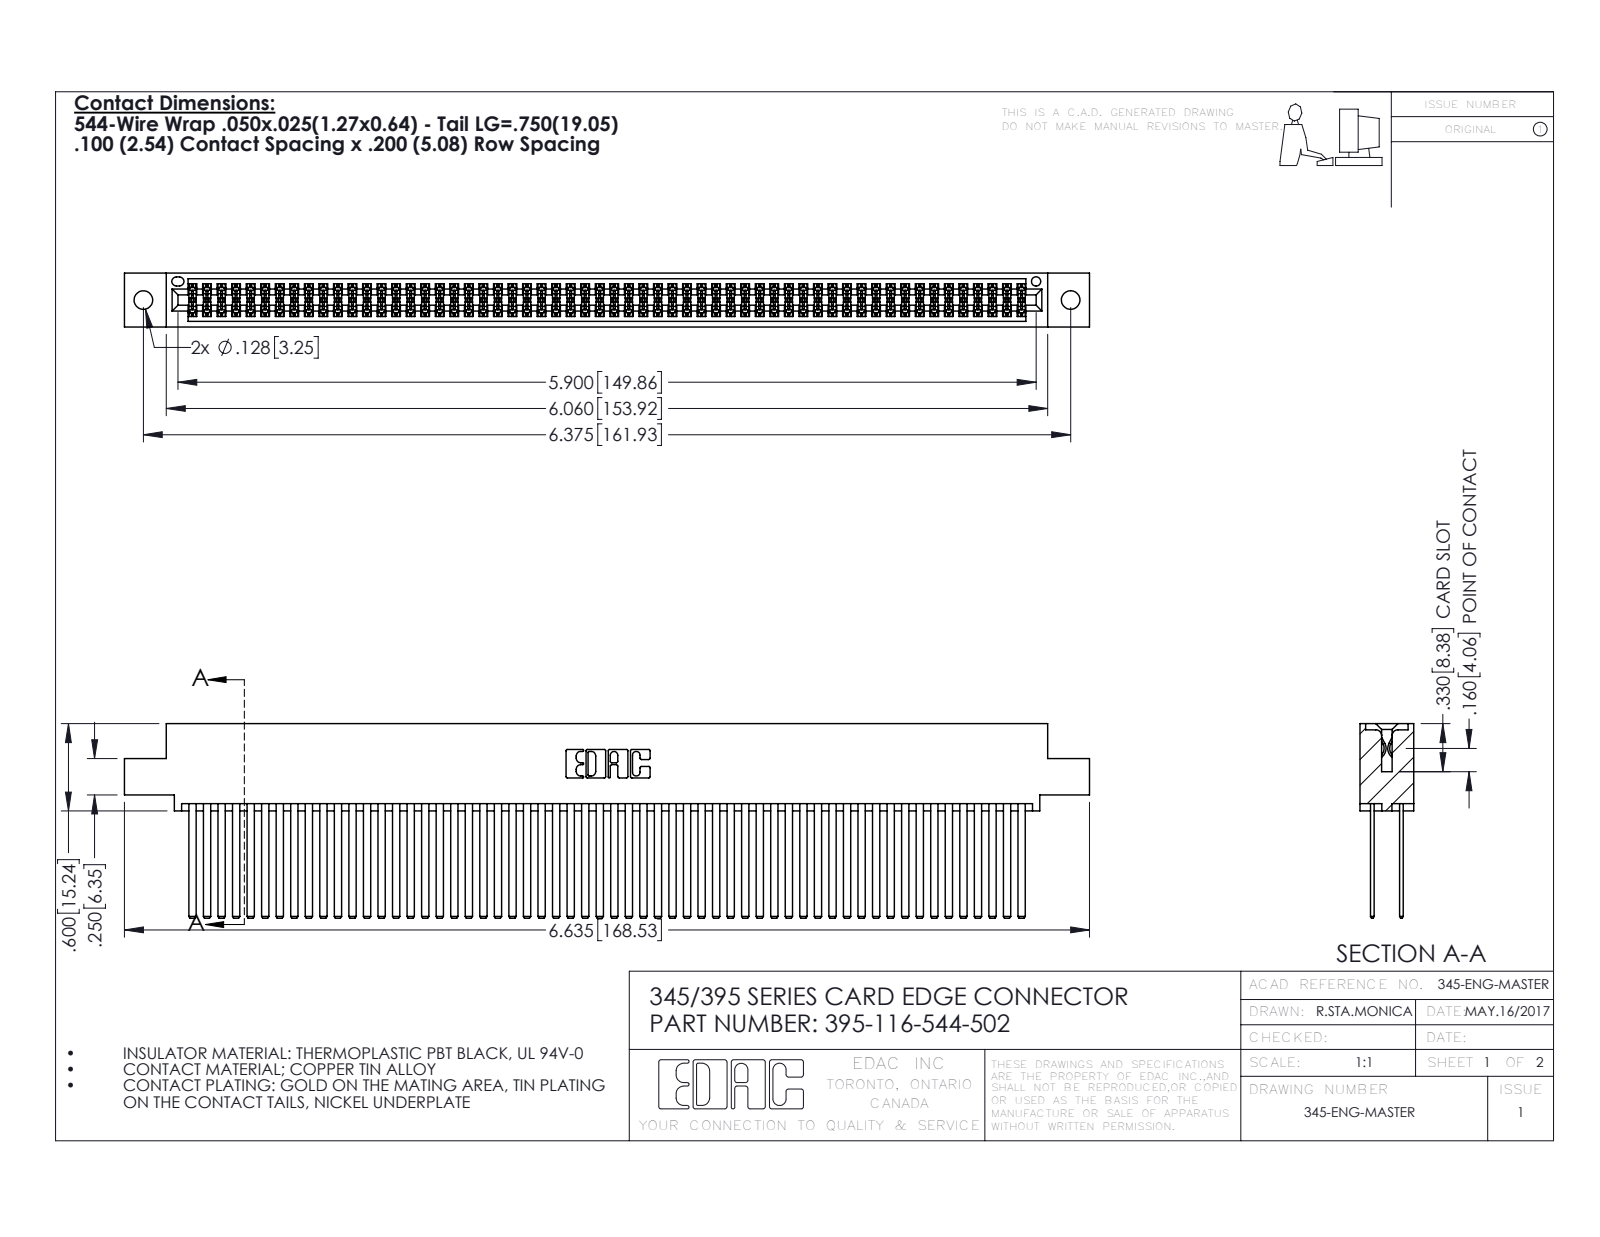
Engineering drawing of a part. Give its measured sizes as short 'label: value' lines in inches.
name: 395-116-544-502; 345 Part_0.110 Offset - 0.128 Dia; 345-292-001_345-293-144
written by: SolidWorks 2016 (CONFIG_CONTROL_DESIGN)
unit: in
bodies: 117 solids, 5234 faces (3448 planar, 1786 cylindrical, 0 other)
size: 6.635 × 1.337 × 0.37
volume: 1.101 in³; area: 48.91 in²
holes: 2× ⌀0.128, 1× ⌀0.064
rounds: 174× R0.006, 22× R0.01, 6× R0.007, 6× R0.031, 3× R0.026, 2× R0.014, 2× R0.019, 2× R0.022
face distances: 0.2, 0.025, 0.298, 0.072, 0.098, 0.272, 0.225, 0.175, 0.37, 0.05
hole spacings: 0.27, 6.139, 6.375
